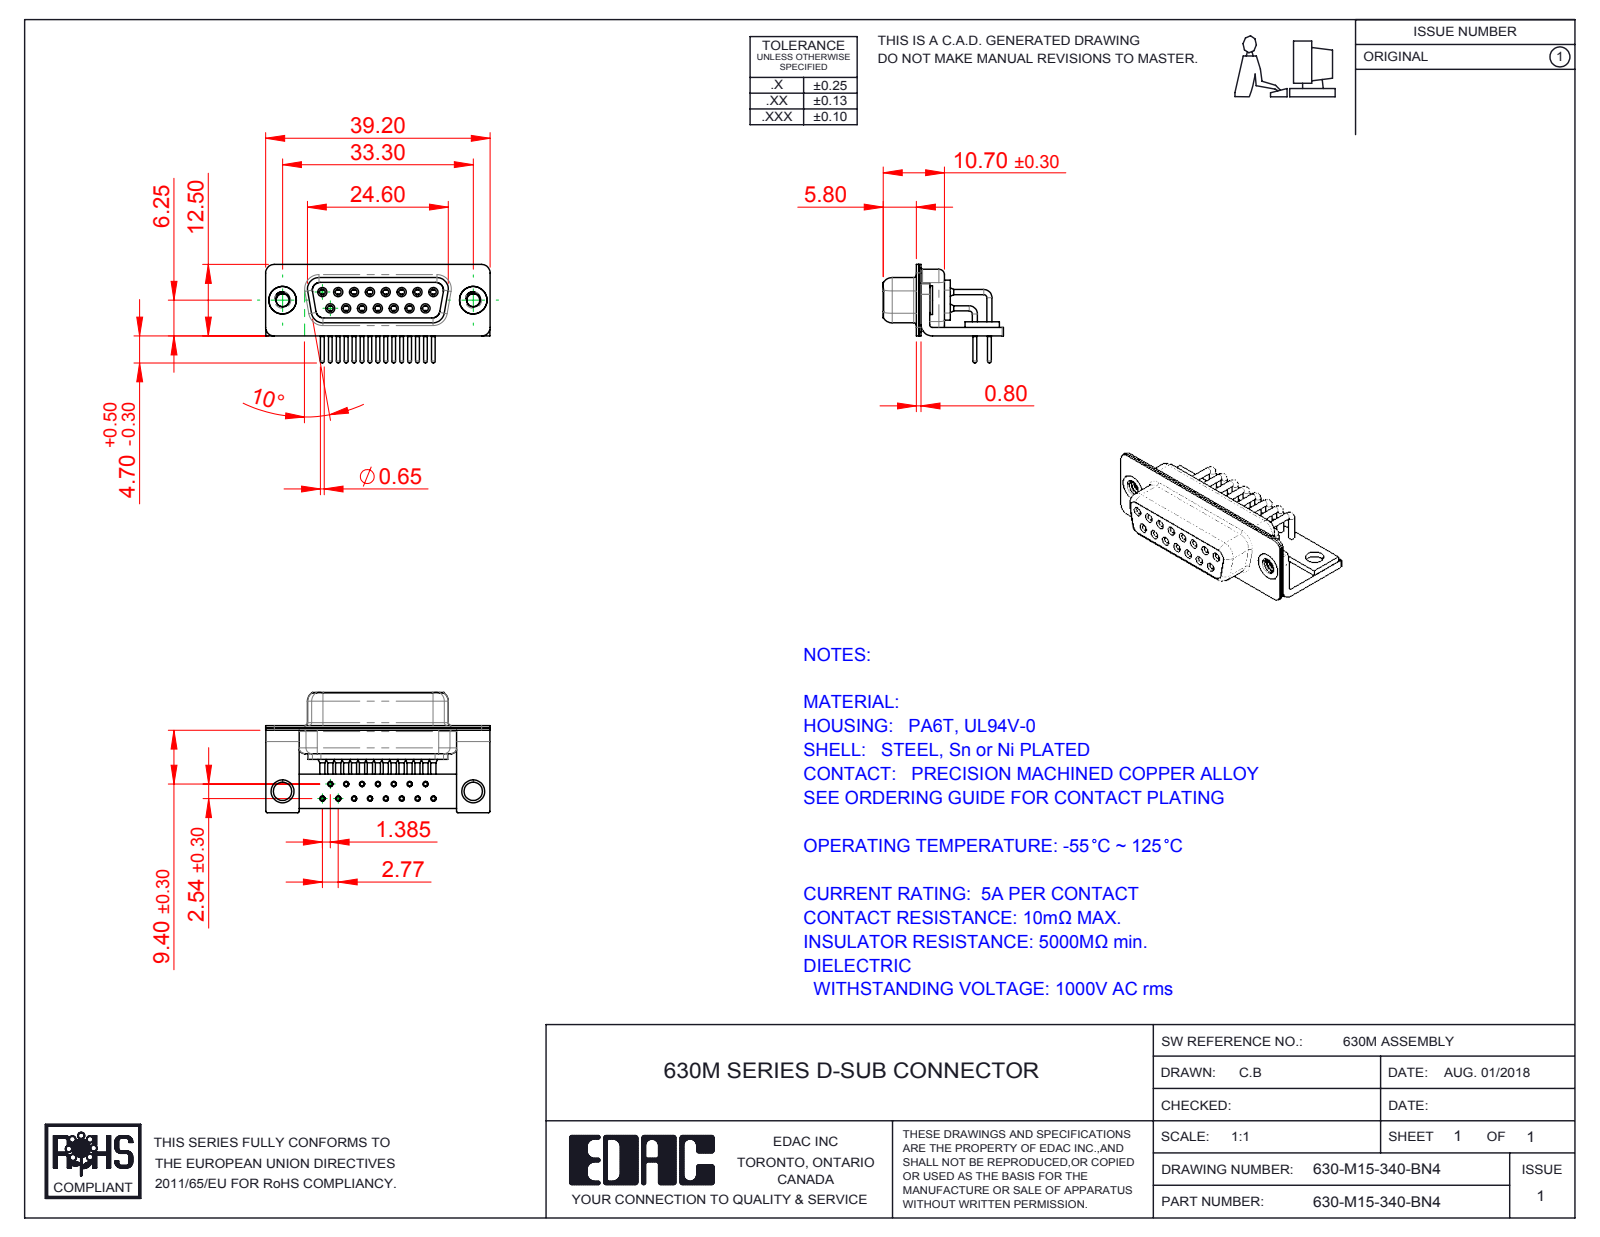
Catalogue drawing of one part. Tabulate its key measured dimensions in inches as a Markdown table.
| quantity | value |
| --- | --- |
| part name | 630M Shell Front_15 Contacts; 630M Stabilizer Board_15 Contacts; 630M Housing_15 Contacts; 630M Shell Rear_15 Contacts (+5 more) |
| STEP written by | SolidWorks 2016 (CONFIG_CONTROL_DESIGN) |
| units | inches |
| bodies | 23 solids, 1154 faces (318 planar, 534 cylindrical, 302 other) |
| overall size | 1.543 × 0.827 × 0.677 |
| volume | 0.186 in³ |
| surface area | 11.96 in² |
| round holes (diameter × count) | 0.035 × 15, 0.039 × 15, 0.043 × 15, 0.067 × 15, 0.071 × 15, 0.079 × 15, 0.089 × 2, 0.126 × 2, 0.157 × 2, 0.189 × 2 |
| round bosses / shafts (diameter × count) | 0.035 × 27, 0.063 × 15, 0.059 × 15, 0.026 × 15, 0.197 × 2, 0.193 × 2 |
| partial cylindrical surfaces (radius × count) | 0.01 × 16, 0.059 × 16, 0.079 × 13, 0.053 × 8, 0.063 × 8, 0.02 × 5, 0.024 × 4, 0.026 × 4 |
| main face-to-face distances | 0.016, 0.031, 0.091, 0.368, 0.075, 0.059, 0.039, 0.057, 0.352, 0.033 |
| hole center spacings | 0.109, 0.218, 0.327, 0.124, 0.192, 0.436, 0.114, 0.29 |
